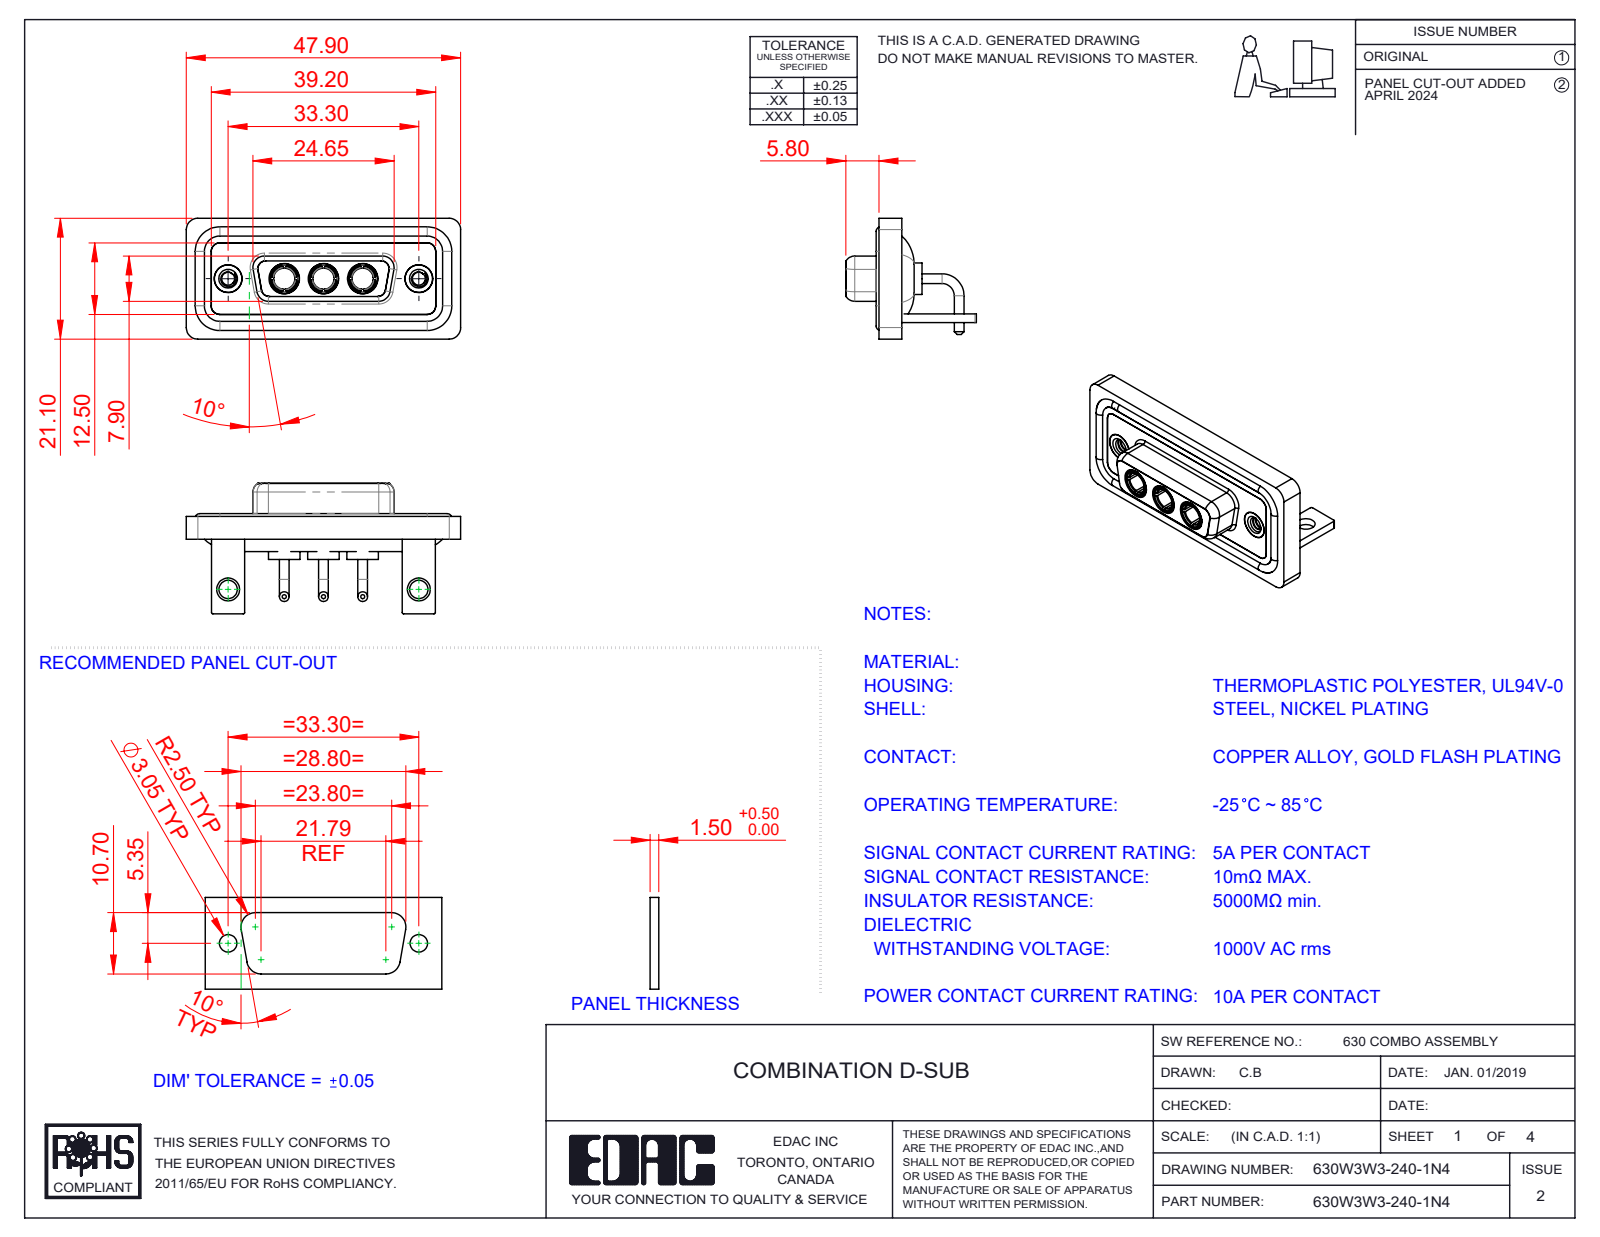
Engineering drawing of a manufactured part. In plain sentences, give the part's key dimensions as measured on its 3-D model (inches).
The part is named "630Combo Shell Rear_15 Contacts; 630Combo Housing_3W3; 630Combo Shell Front_15 Contacts; 630W3W3-240-1N4 (+4 more)". Its 3-D file was written by "SolidWorks 2023 (CONFIG_CONTROL_DESIGN)". It is 15 solids with 668 faces: 212 planar, 287 cylindrical and 169 other. Overall it measures 1.886 by 0.898 by 0.831 inches. Its volume is 0.389 cubic inches and its surface area 16.36 square inches. Round holes: 5 of diameter 0.191, 3 of diameter 0.146, 3 of diameter 0.209, 2 of diameter 0.089, 2 of diameter 0.126, 2 of diameter 0.157, 2 of diameter 0.159, 2 of diameter 0.197. Round bosses or shafts: 6 of diameter 0.067, 4 of diameter 0.063, 3 of diameter 0.217, 3 of diameter 0.205, 3 of diameter 0.195, 3 of diameter 0.187, 3 of diameter 0.148, 2 of diameter 0.195. Partial cylindrical surfaces (rounded edges, fillets, slot ends): 21 of radius 0.079, 18 of radius 0.059, 16 of radius 0.01, 12 of radius 0.053, 8 of radius 0.063, 5 of radius 0.02, 4 of radius 0.024, 4 of radius 0.026. The main face-to-face distances are 0.016, 0.114, 0.059, 0.071, 0.146, 0.043, 0.161, 0.063, 0.098, 0.055. The hole center spacings are 0.27, 0.386, 0.656, 0.925, 1.311, 0.539.
